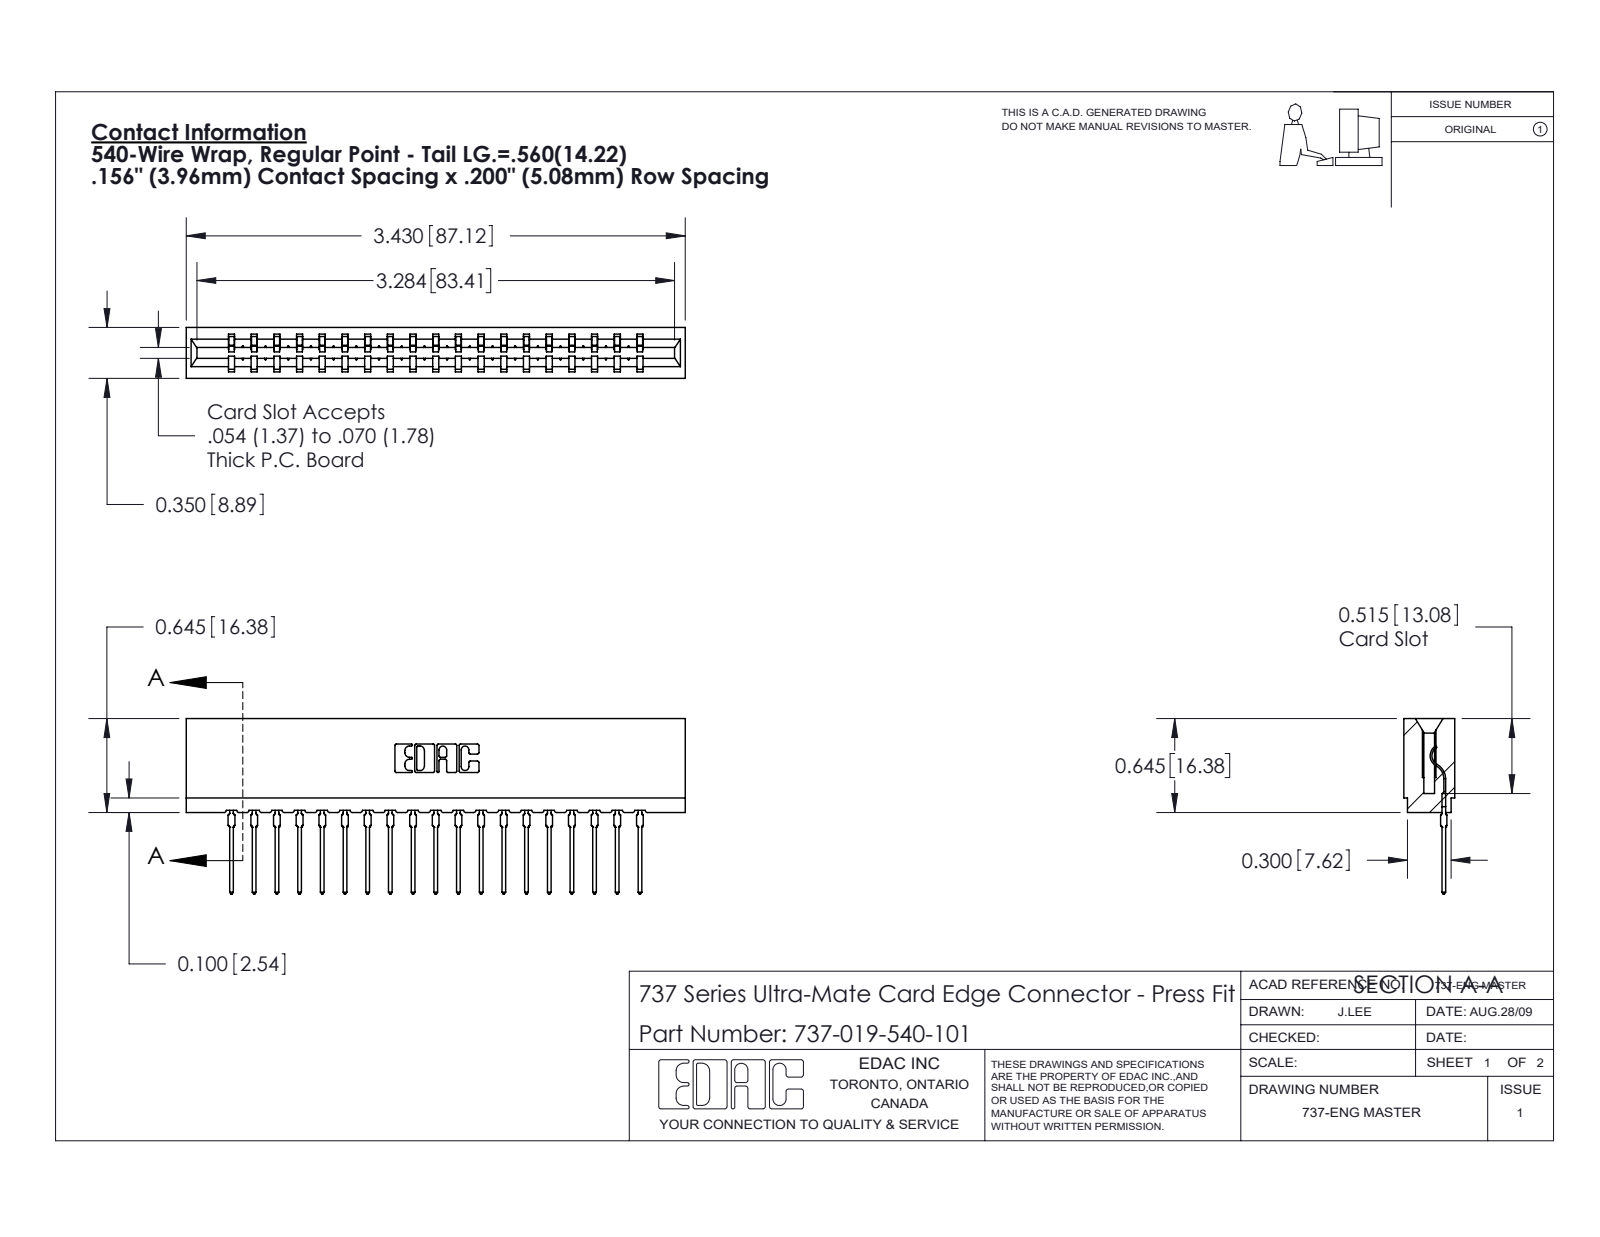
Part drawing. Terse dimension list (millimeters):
name: 737 Part_Insulator Option - 01; 737-019-540-101; 745-292-001_540
written by: SolidWorks 2020 (CONFIG_CONTROL_DESIGN)
unit: mm
bodies: 20 solids, 2241 faces (1346 planar, 401 cylindrical, 494 other)
size: 87.1 × 30.6 × 8.9
volume: 8 620 mm³; area: 11 390 mm²
rounds: 38× R0.4, 38× R0.5, 22× R0.3, 6× R0.2, 6× R0.8, 4× R0.1, 4× R0.3, 3× R0.7
face distances: 3.5, 5.4, 8.9, 4, 15.8, 19.8, 11.9, 1.9, 7.9, 35.7
